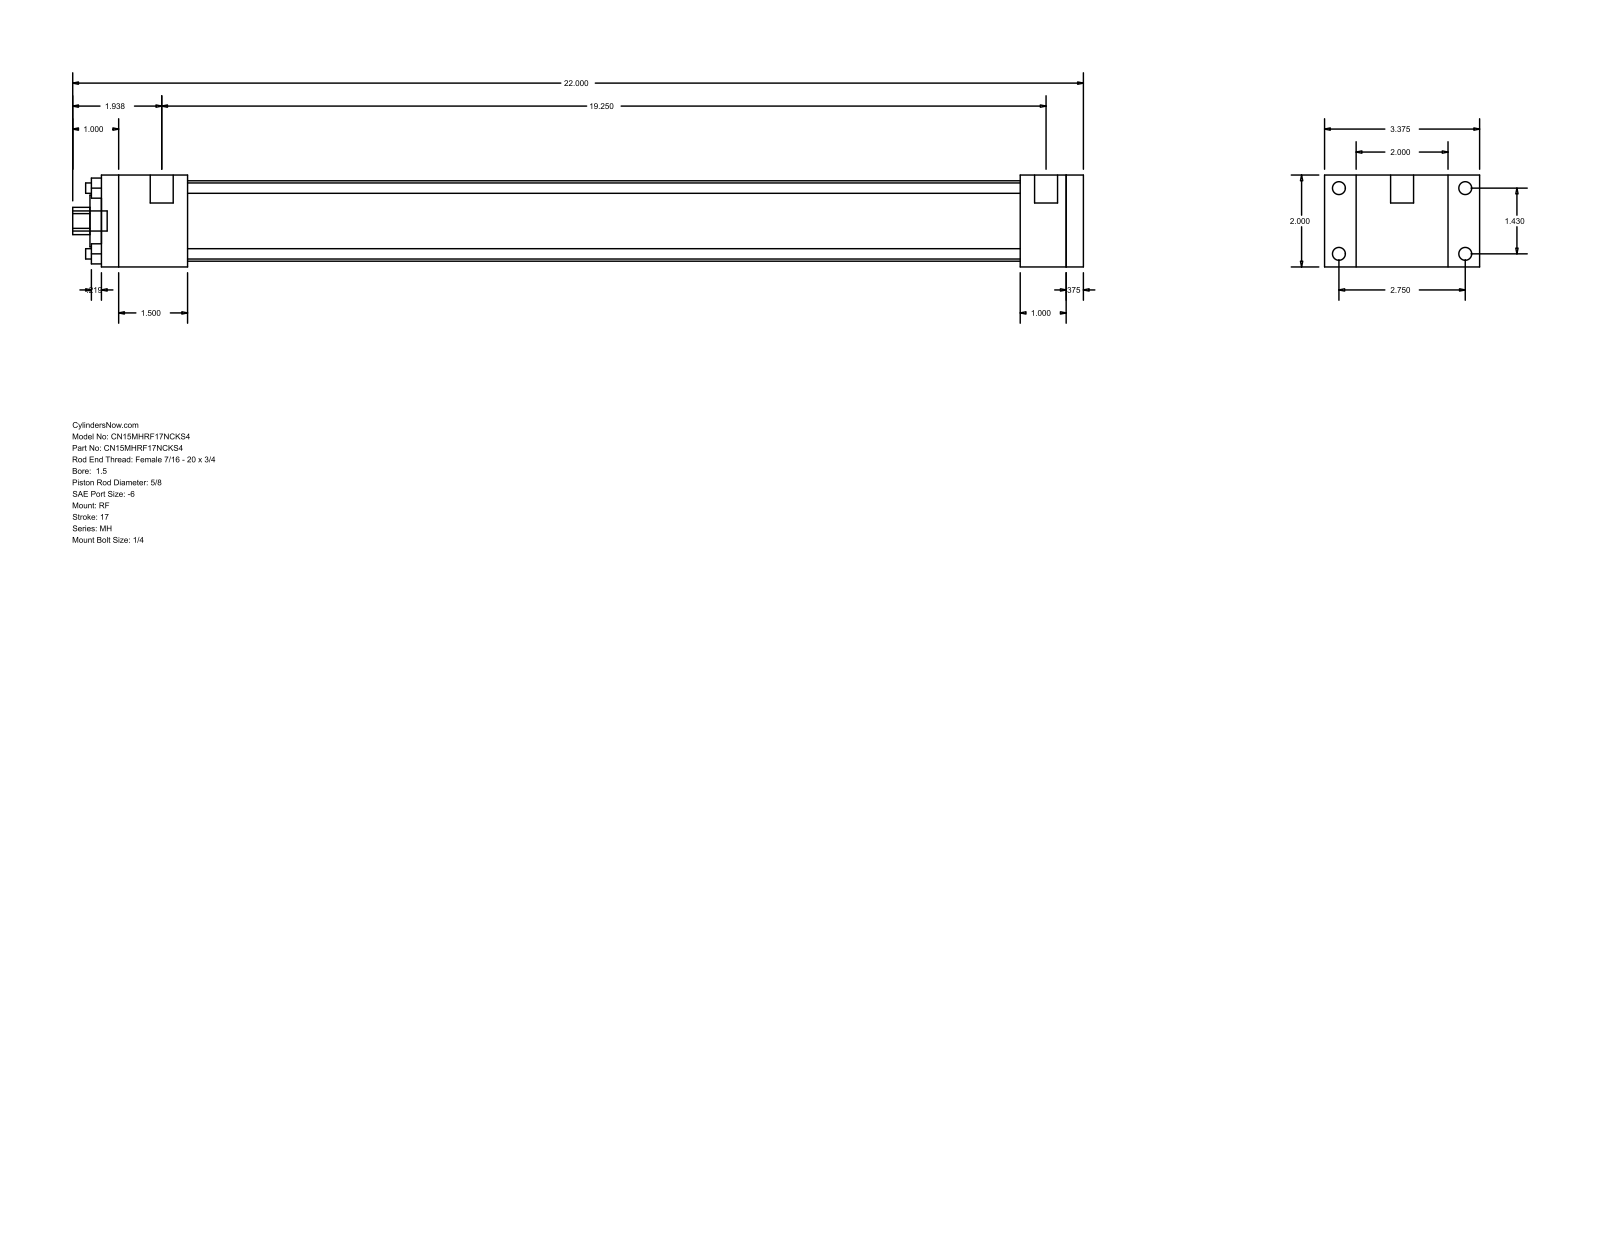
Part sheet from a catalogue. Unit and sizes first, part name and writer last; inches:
Units: inches
Overall size (bounding box): 22 × 3.375 × 2
Round holes (diameter × count): ⌀0.225 ×4, ⌀0.625 ×1, ⌀1.125 ×1, ⌀1.75 ×1
Round bosses / shafts (diameter × count): ⌀0.281 ×4, ⌀0.219 ×4, ⌀0.5 ×2, ⌀0.437 ×1
Partial cylindrical surfaces — rounded edges, fillets, slot ends (radius × count): R0.297 ×1
Main face-to-face distances: 2, 0.375, 21.375, 21, 0.687, 2.687, 20, 1, 1.375, 1.875
Hole centre spacings: 1.011, 1.43, 2.022
Bodies: 0 solids, 92 faces (64 planar, 28 cylindrical, 0 other)
Part name (STEP PRODUCT): MH_RF__0150_0.625
STEP written by: GSSL Pune (CONFIG_CONTROL_DESIGN)
